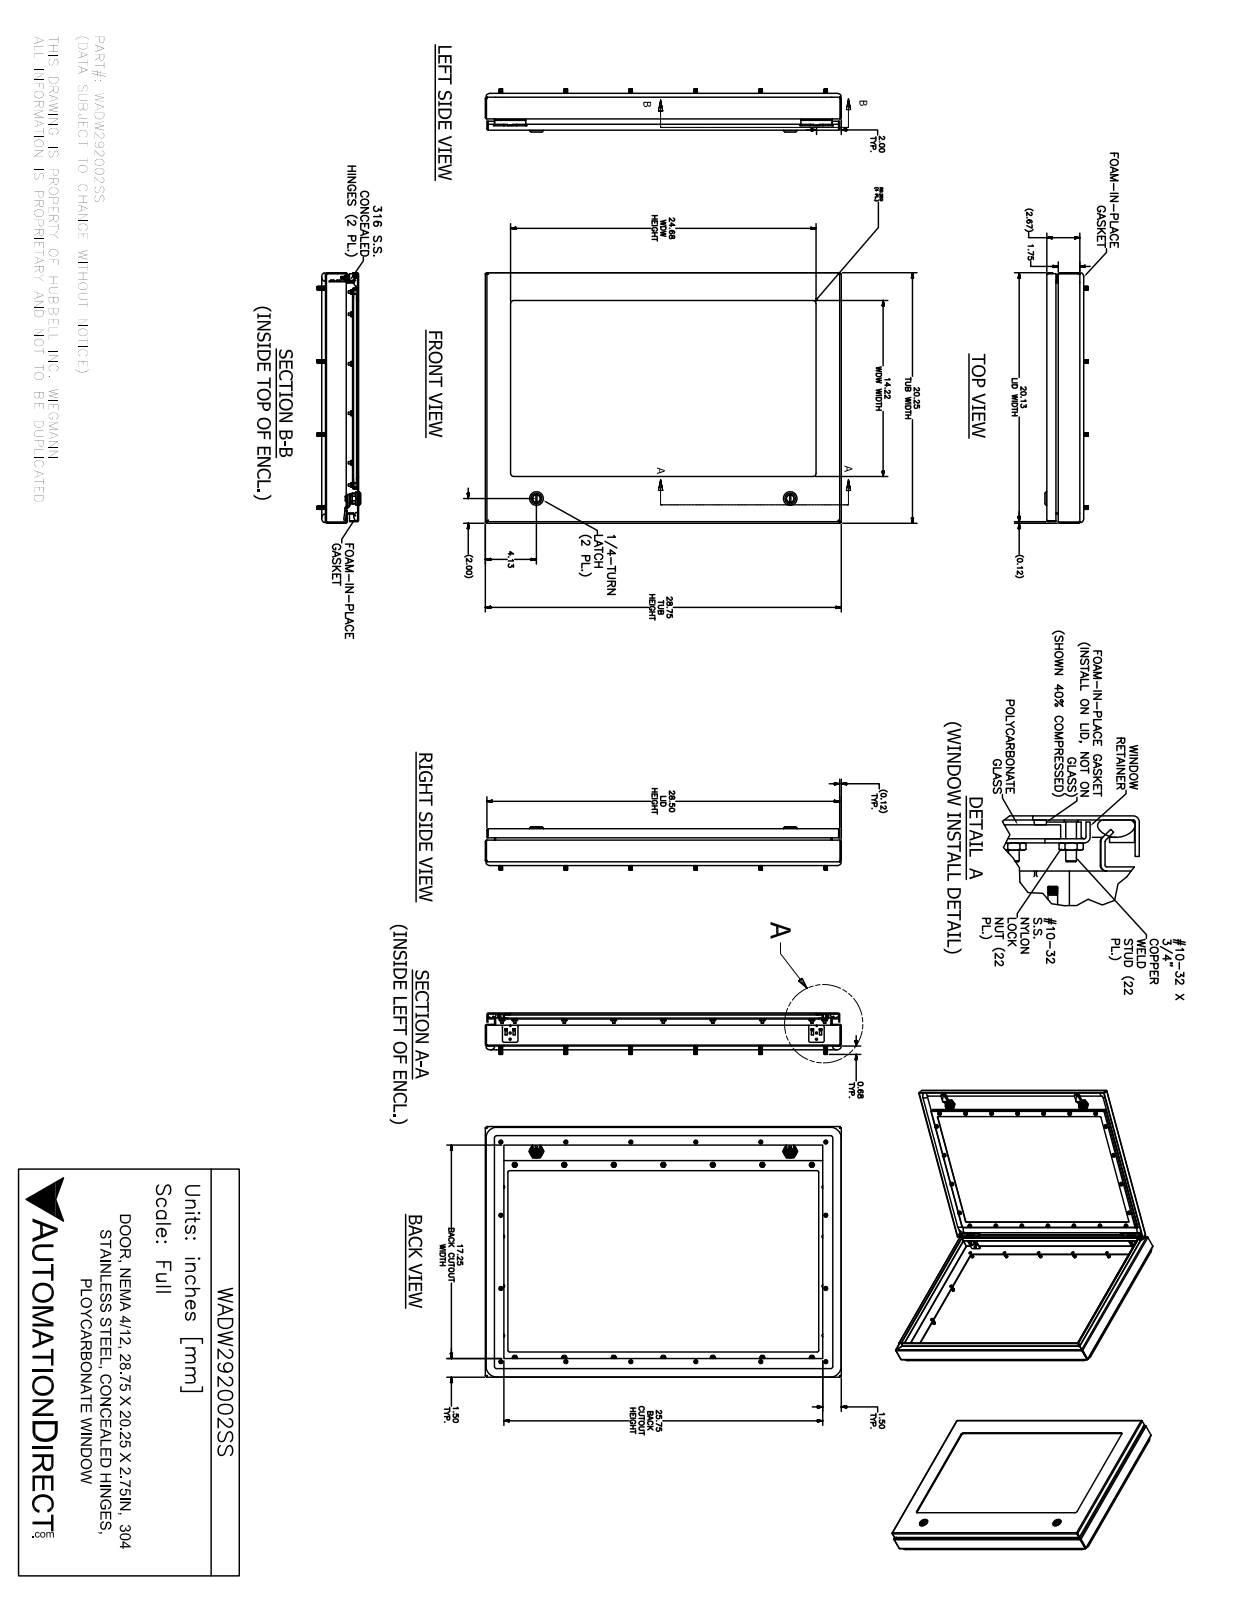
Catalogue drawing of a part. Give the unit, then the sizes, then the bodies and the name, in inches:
Units: inches
Overall size (bounding box): 28.75 × 20.25 × 3.501
Round holes (diameter × count): ⌀0.156 ×24, ⌀0.281 ×22, ⌀0.249 ×16, ⌀0.093 ×4, ⌀0.152 ×4, ⌀0.167 ×4, ⌀0.172 ×4, ⌀0.188 ×4, ⌀0.197 ×2, ⌀0.315 ×2, ⌀0.394 ×2, ⌀0.402 ×2
Round bosses / shafts (diameter × count): ⌀0.25 ×46, ⌀0.19 ×22, ⌀0.32 ×16, ⌀0.313 ×16, ⌀0.188 ×16, ⌀0.36 ×4, ⌀0.32 ×4, ⌀0.256 ×4
Partial cylindrical surfaces — rounded edges, fillets, slot ends (radius × count): R0.012 ×54, R0.031 ×34, R0.05 ×26, R0.105 ×24, R0.02 ×23, R0.125 ×20, R0.016 ×18, R0.032 ×8
Main face-to-face distances: 0.074, 0.25, 2.593, 0.337, 0.087, 0.411, 0.161, 2.182, 2.256, 2.506
Hole centre spacings: 5.25, 18.51, 10.5, 20.623, 15.75, 17.75, 23.73, 26.909
Volume: 194 in³ · Surface area: 2 904 in²
Bodies: 101 solids, 3108 faces (1106 planar, 1072 cylindrical, 930 other)
Part name (STEP PRODUCT): WADW292002
STEP written by: SolidWorks 2017 (AUTOMOTIVE_DESIGN)
